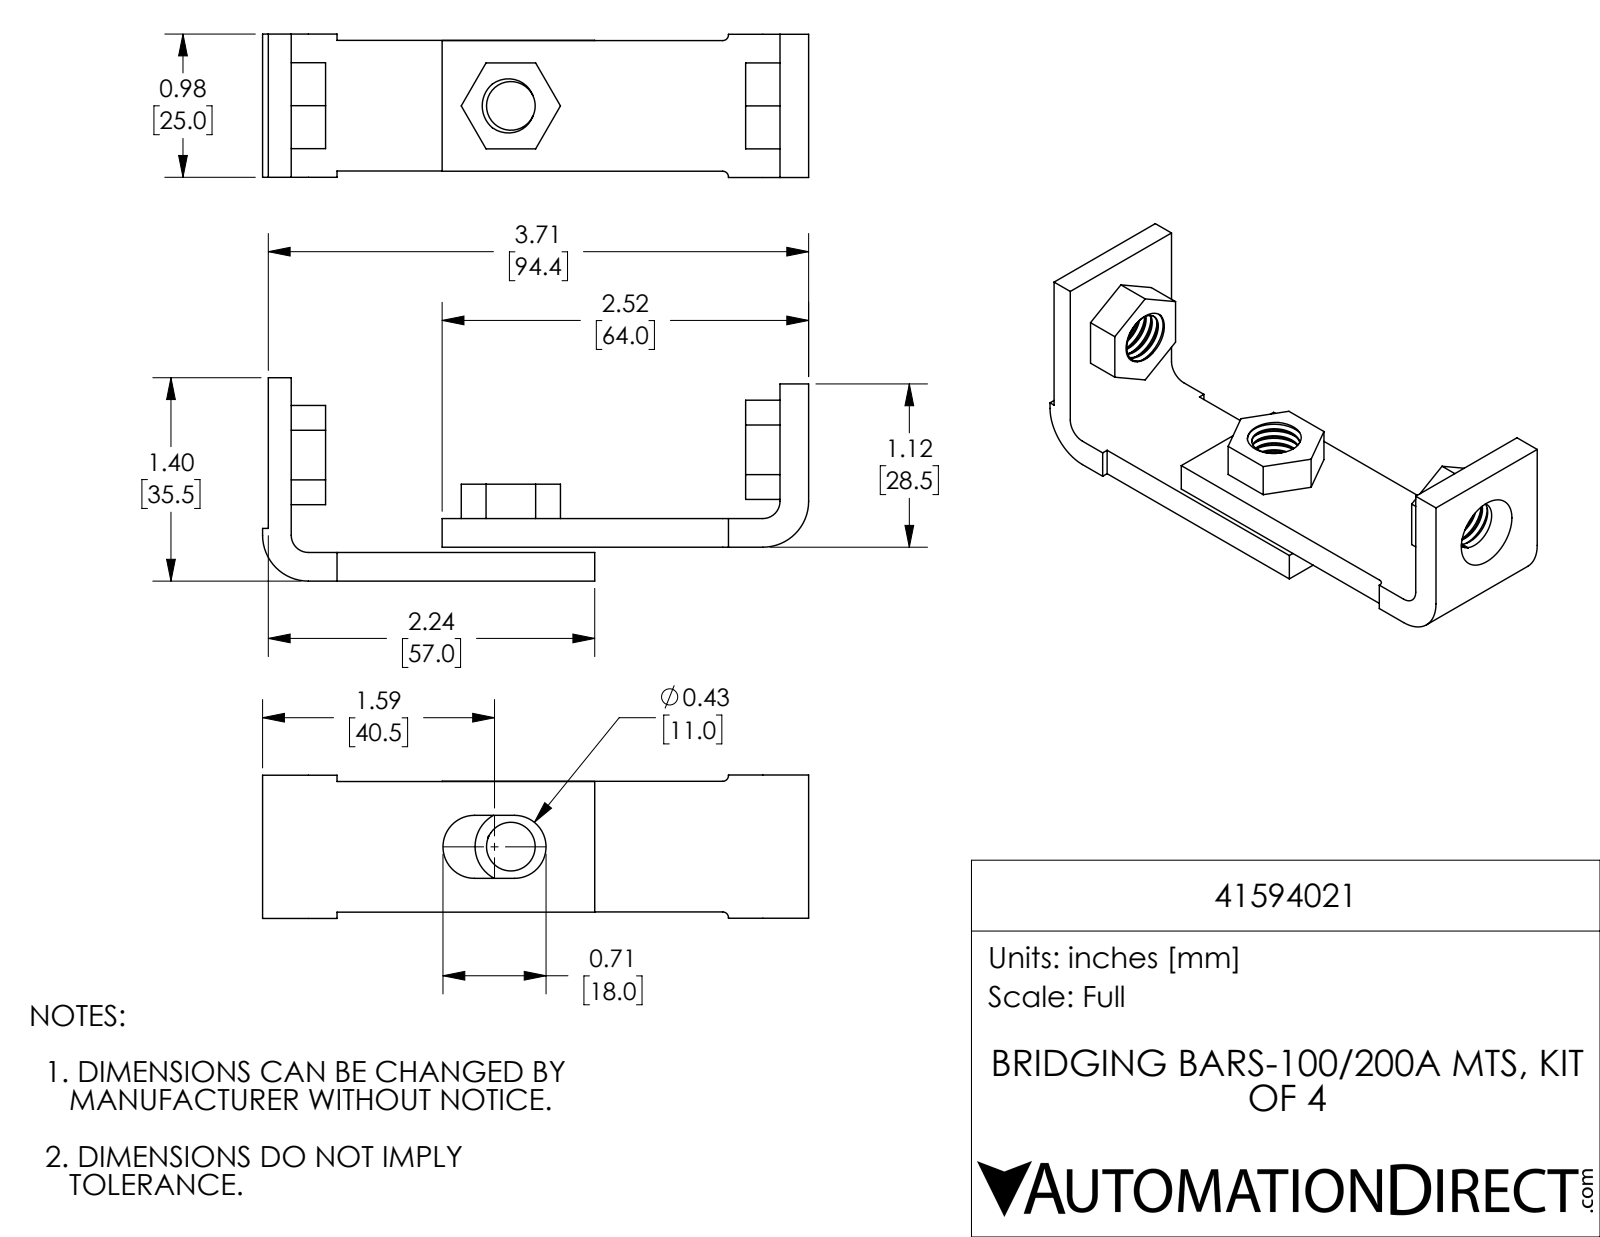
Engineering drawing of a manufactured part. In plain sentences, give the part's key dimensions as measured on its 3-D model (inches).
The part is named "41594021". Its 3-D file was written by "SolidWorks 2017 (AUTOMOTIVE_DESIGN)". It is 5 solids with 154 faces: 58 planar, 90 cylindrical and 6 other. Overall it measures 3.754 by 1.398 by 0.986 inches. Its volume is 1.208 cubic inches and its surface area 20.25 square inches. Round holes: 3 of diameter 0.335, 3 of diameter 0.394, 3 of diameter 0.492. Round bosses or shafts: 3 of diameter 0.512. Partial cylindrical surfaces (rounded edges, fillets, slot ends): 2 of radius 0.039, 2 of radius 0.118, 2 of radius 0.217, 2 of radius 0.315. The main face-to-face distances are 0.197, 0.233, 0.43, 0.036, 0.043, 0.941, 0.157, 3.518, 0.898, 0.591. The hole center spacings are 0.036.
